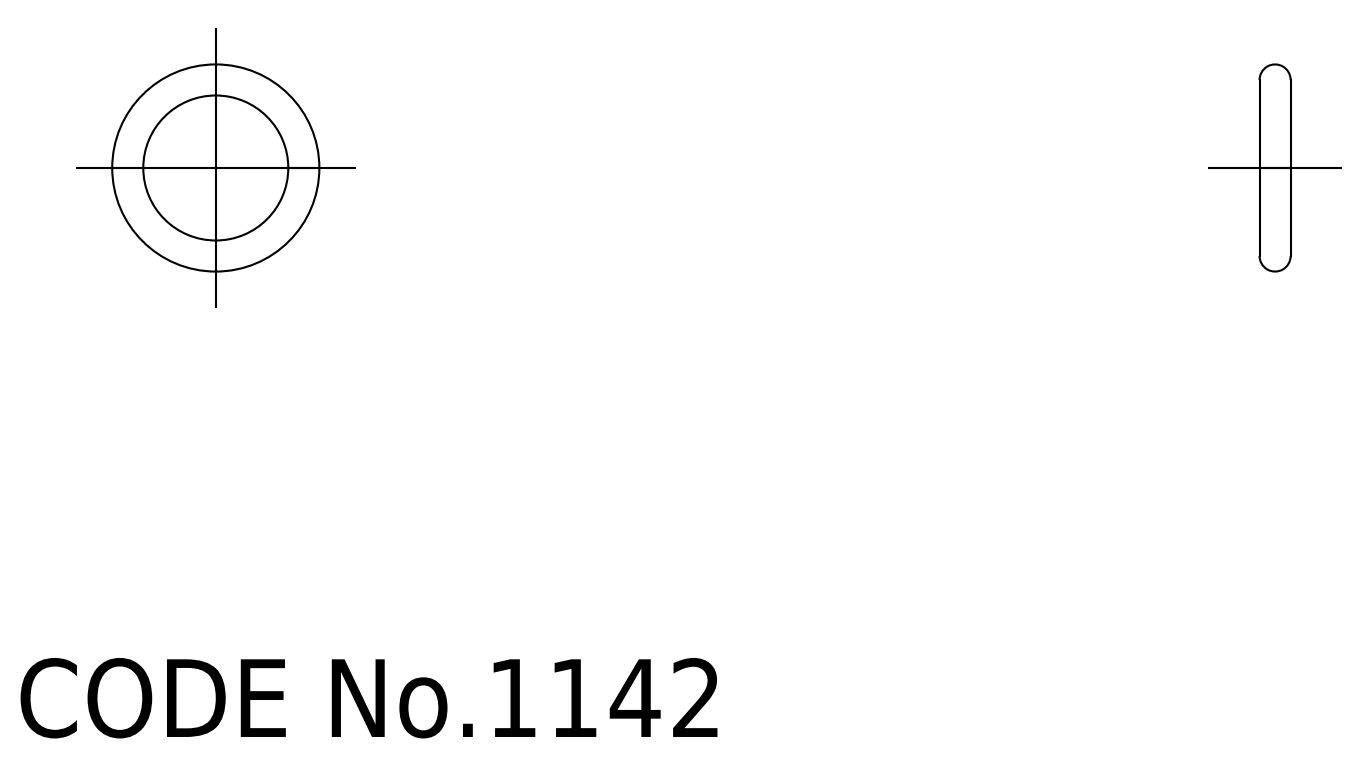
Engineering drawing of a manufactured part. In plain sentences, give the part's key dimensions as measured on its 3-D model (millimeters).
The part is named "67109293". Its 3-D file was written by "CADfix (AUTOMOTIVE_DESIGN)". It is 1 solid with 4 faces: 0 planar, 0 cylindrical and 4 other. Overall it measures 8 by 8 by 1.2 millimeters. Its volume is 24 cubic millimeters and its surface area 81 square millimeters.
